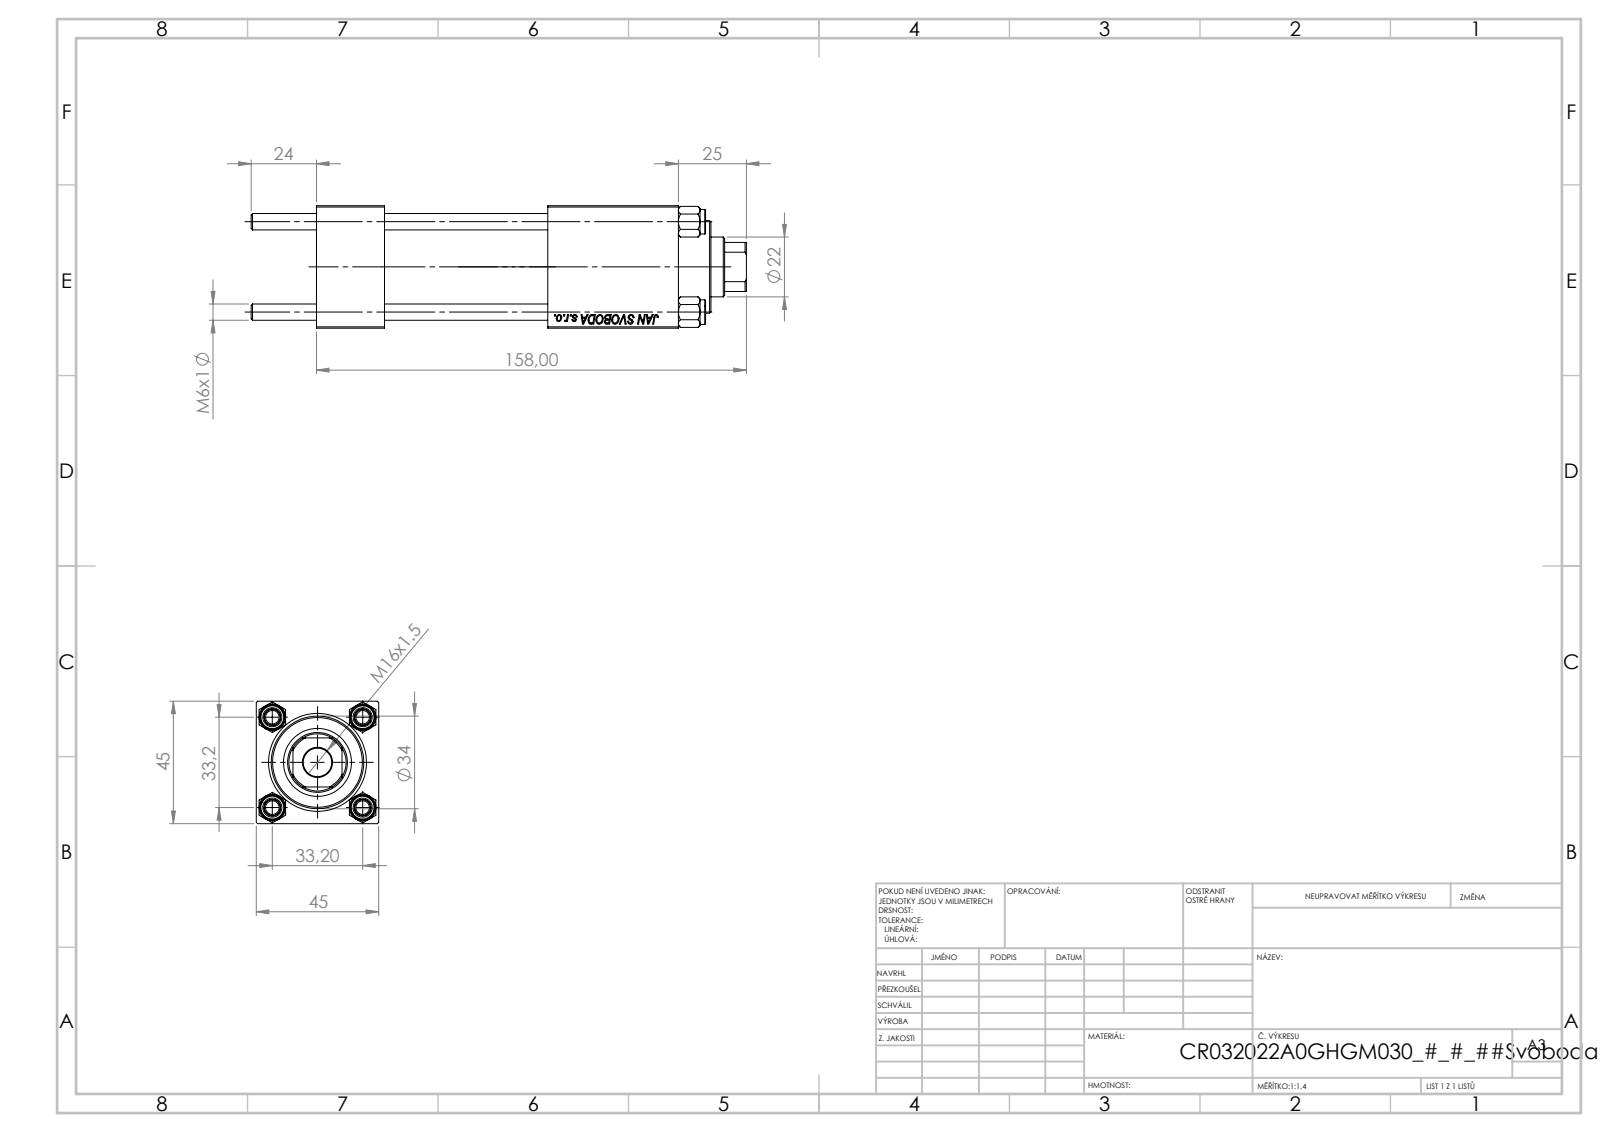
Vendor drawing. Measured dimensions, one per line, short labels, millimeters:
name: V215CR_BODY_A; CR025_012_A_0_G_A_G_M_020_+#_##_TYCINKA; V215_VC_A; NUT_M5 (+1 more)
written by: SolidWorks 2019 (CONFIG_CONTROL_DESIGN)
unit: mm
bodies: 11 solids, 1133 faces (519 planar, 78 cylindrical, 536 other)
size: 182 × 45 × 45
volume: 222 505 mm³; area: 80 686 mm²
holes: 4× ⌀6, 2× ⌀7, 2× ⌀13.16, 2× ⌀20, 1× ⌀10.5, 1× ⌀22, 1× ⌀24, 1× ⌀25, 1× ⌀32, 1× ⌀33
bosses: 4× ⌀9, 1× ⌀38, 1× ⌀34
rounds: 1× R10.5
face distances: 45, 25, 60, 133, 85, 108, 48, 30, 104.3, 79.3
hole spacings: 23.48, 33.2, 46.95, 85.5
